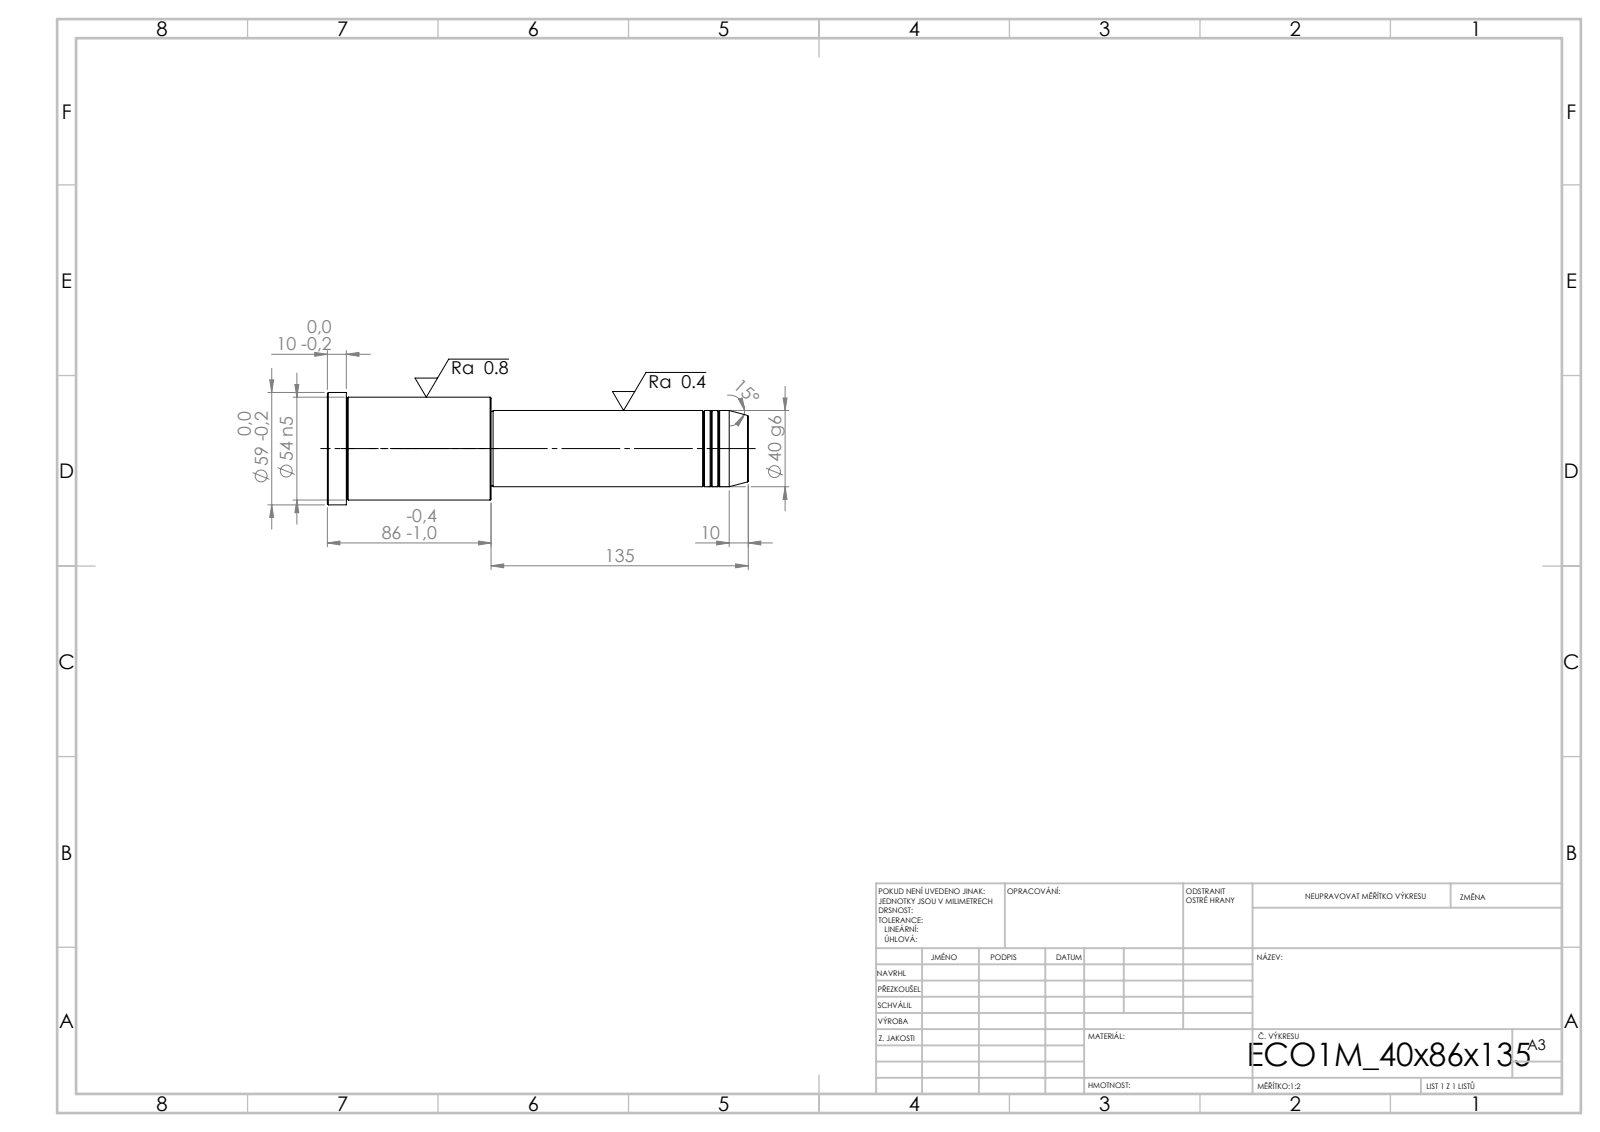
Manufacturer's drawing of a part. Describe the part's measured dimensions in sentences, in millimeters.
Its 3-D file was written by "SolidWorks 2019 (CONFIG_CONTROL_DESIGN)". It is 1 solid with 43 faces: 5 planar, 14 cylindrical and 24 other. Overall it measures 221 by 59 by 59 millimeters. Its volume is 369 112 cubic millimeters and its surface area 37 126 square millimeters. Round bosses or shafts: 1 of diameter 59, 1 of diameter 54, 1 of diameter 40, 1 of diameter 39. The main face-to-face distances are 86, 135, 221, 211, 76, 10, 134, 1, 77, 87.
